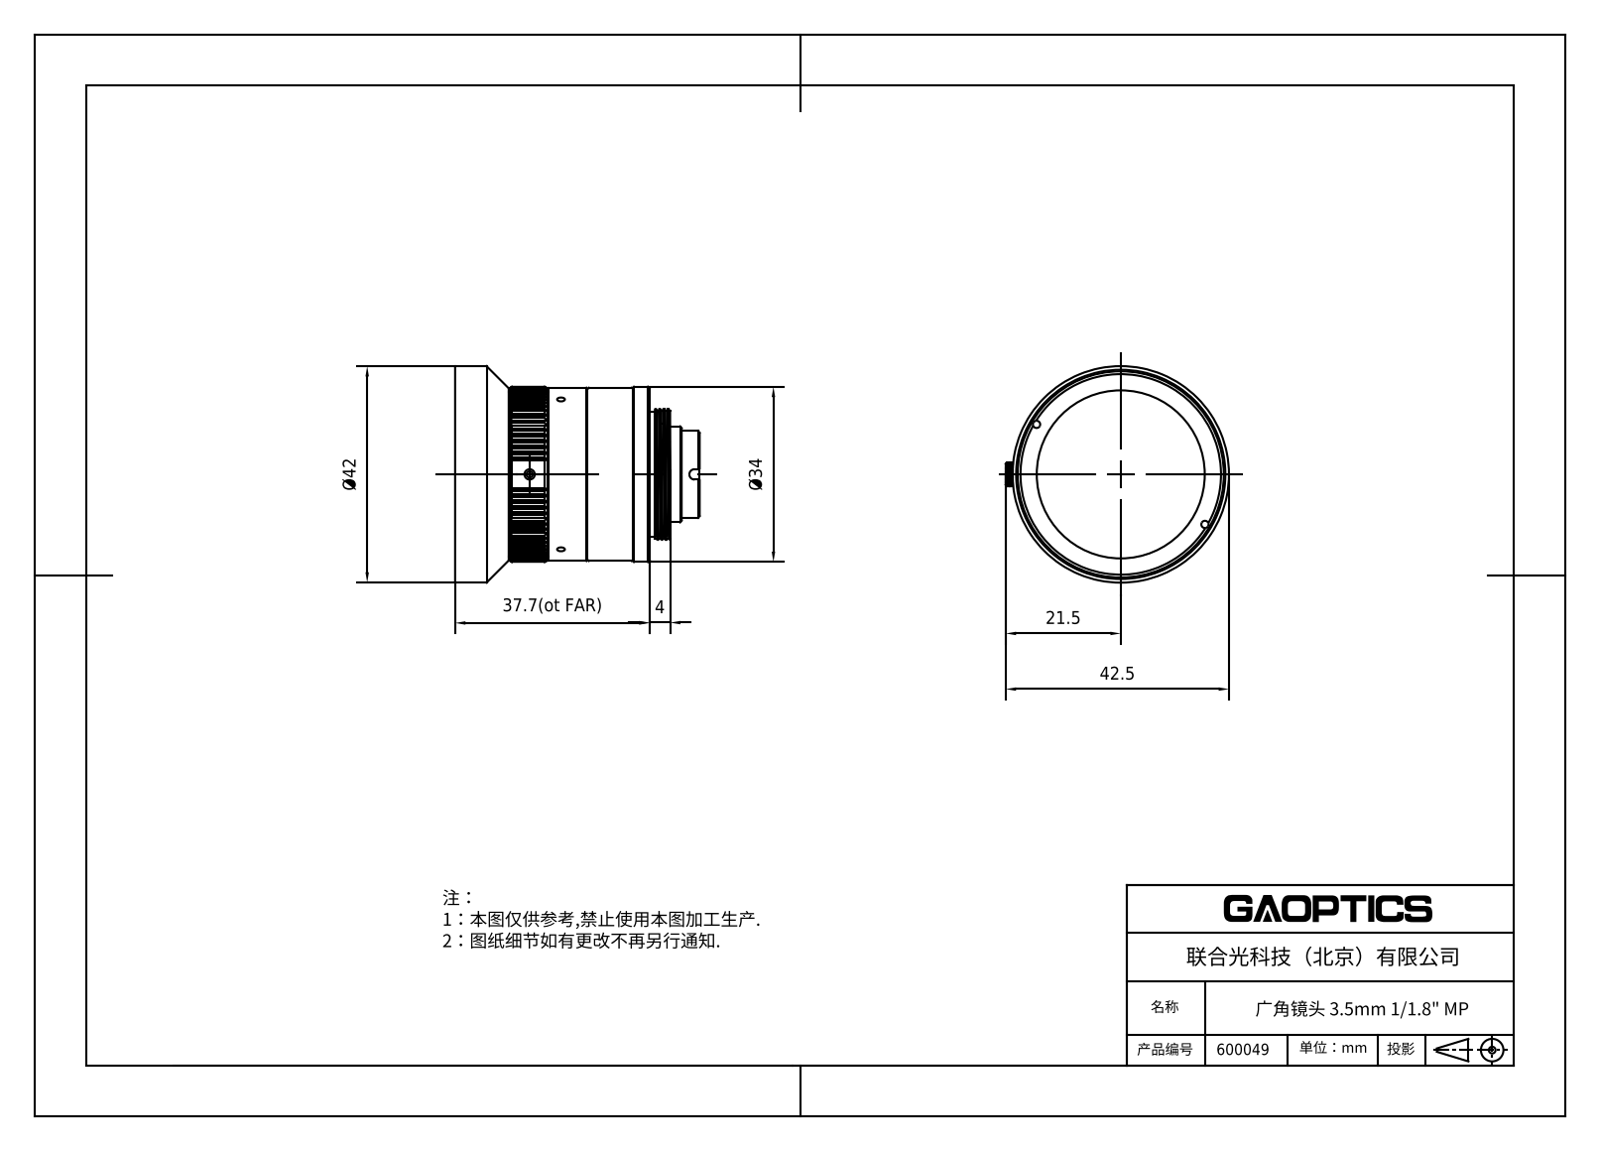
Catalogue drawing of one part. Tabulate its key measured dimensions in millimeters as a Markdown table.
| quantity | value |
| --- | --- |
| part name | 600049 |
| STEP written by | SolidWorks 2020 (CONFIG_CONTROL_DESIGN) |
| units | millimeters |
| bodies | 2 solids, 680 faces (270 planar, 205 cylindrical, 205 other) |
| overall size | 47.46 × 43.32 × 42 |
| volume | 33 147 mm³ |
| surface area | 17 433 mm² |
| round holes (diameter × count) | 1.2 × 4, 2.1 × 3, 1.4 × 2, 1.5 × 2, 2 × 1, 11.5 × 1, 15.3 × 1, 16.6 × 1, 21.4 × 1, 31 × 1, 32.2 × 1, 32.6 × 1 |
| round bosses / shafts (diameter × count) | 2 × 2, 42 × 1, 35.5 × 1, 34 × 1, 33.6 × 1, 32.1 × 1, 32 × 1, 30.7 × 1 |
| partial cylindrical surfaces (radius × count) | 1 × 2, 2.25 × 2 |
| main face-to-face distances | 29.88, 29, 32.13, 2.25, 0.88, 31.25, 33.98, 33.1, 4.1, 1.85 |
| hole center spacings | 13.95, 19, 24.16, 9.67, 9.99, 23.44, 23.71, 24.17 |
